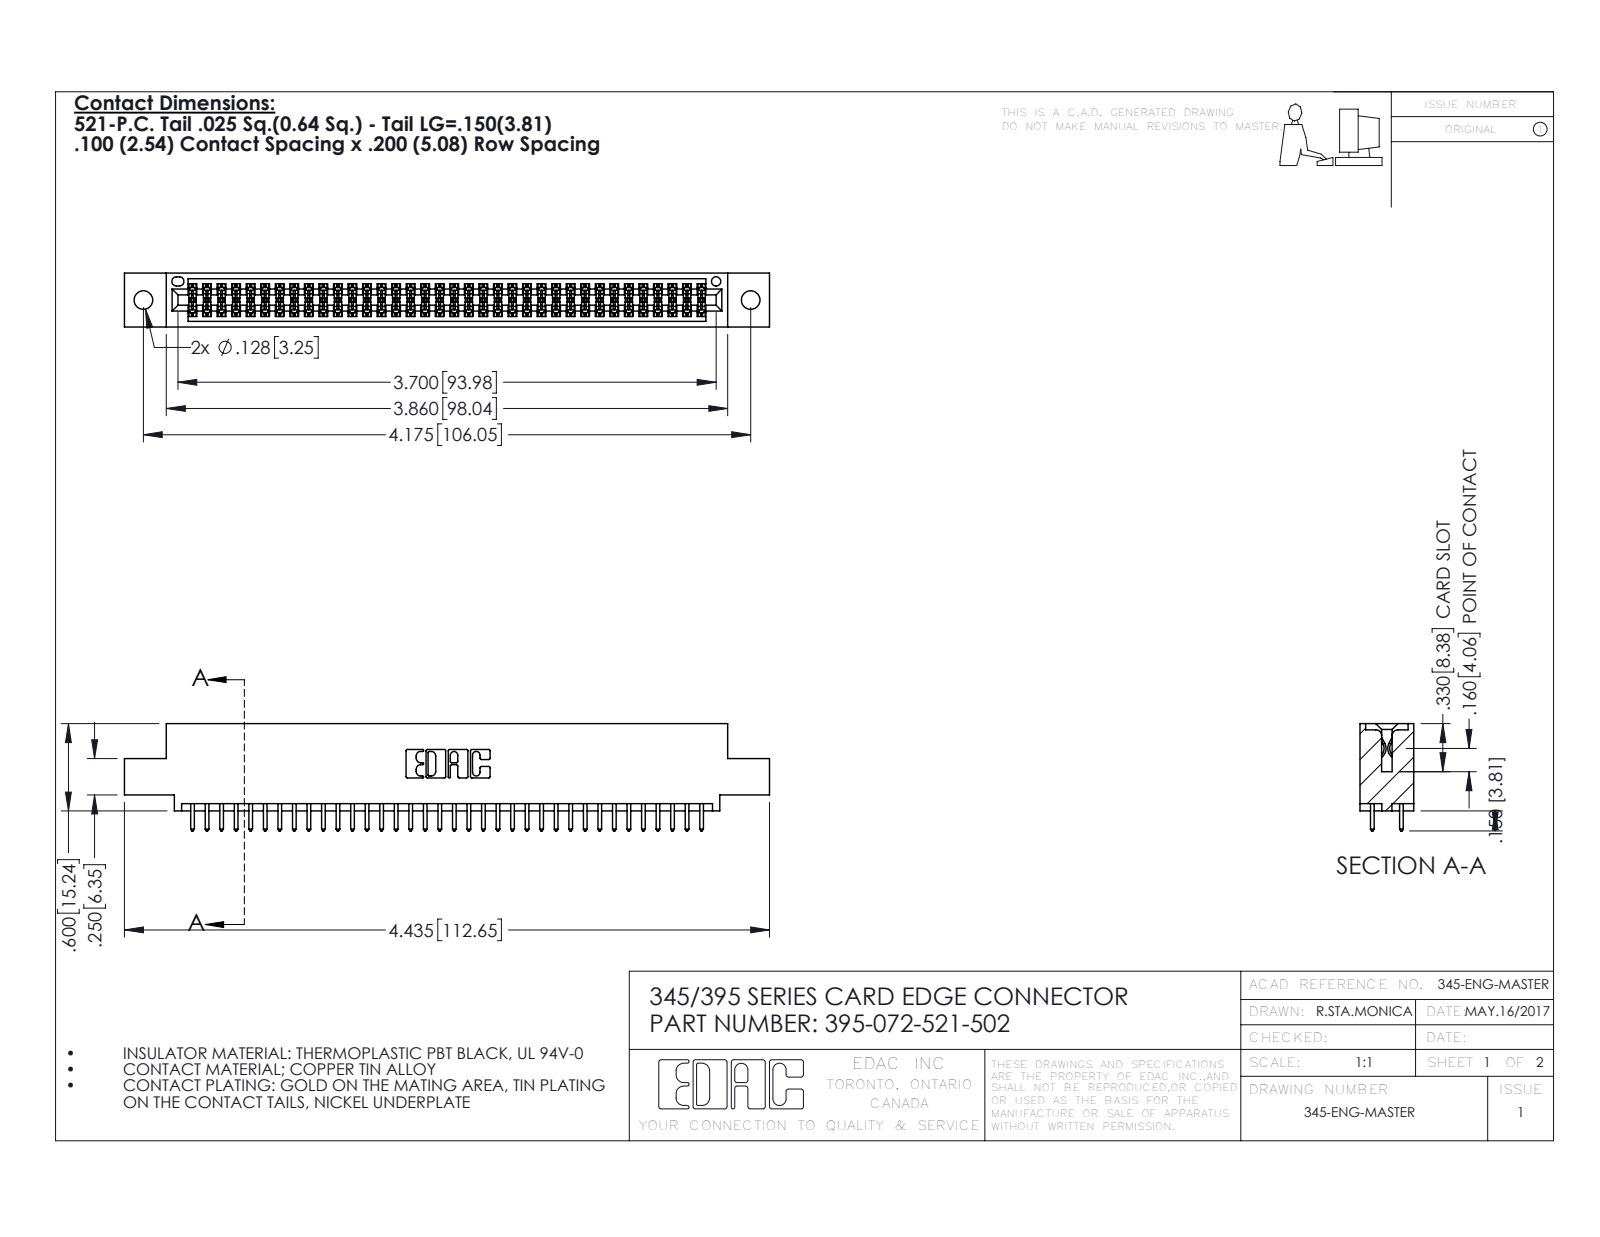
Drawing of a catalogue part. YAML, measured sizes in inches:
part_name: "345-292-001_345-293-121; 345 Part_0.110 Offset - 0.128 Dia; 395-072-521-502"
step_written_by: "SolidWorks 2016 (CONFIG_CONTROL_DESIGN)"
units: inches
bodies: {solids: 73, faces: 3730, planar: 2460, cylindrical: 1270, other: 0}
overall_size: [4.435, 0.737, 0.37]
volume: 0.656
surface_area: 23.87
round_holes:
  - {diameter: 0.128, count: 2}
  - {diameter: 0.064, count: 1}
partial_cylinders:
  - {radius: 0.006, count: 108}
  - {radius: 0.01, count: 72}
  - {radius: 0.01, count: 22}
  - {radius: 0.007, count: 6}
  - {radius: 0.031, count: 6}
  - {radius: 0.026, count: 3}
  - {radius: 0.014, count: 2}
  - {radius: 0.019, count: 2}
face_to_face_distances: [0.298, 0.072, 0.2, 0.37, 0.098, 0.272, 0.025, 0.225, 0.175, 0.149]
hole_center_spacings: [0.27, 3.939, 4.175]
